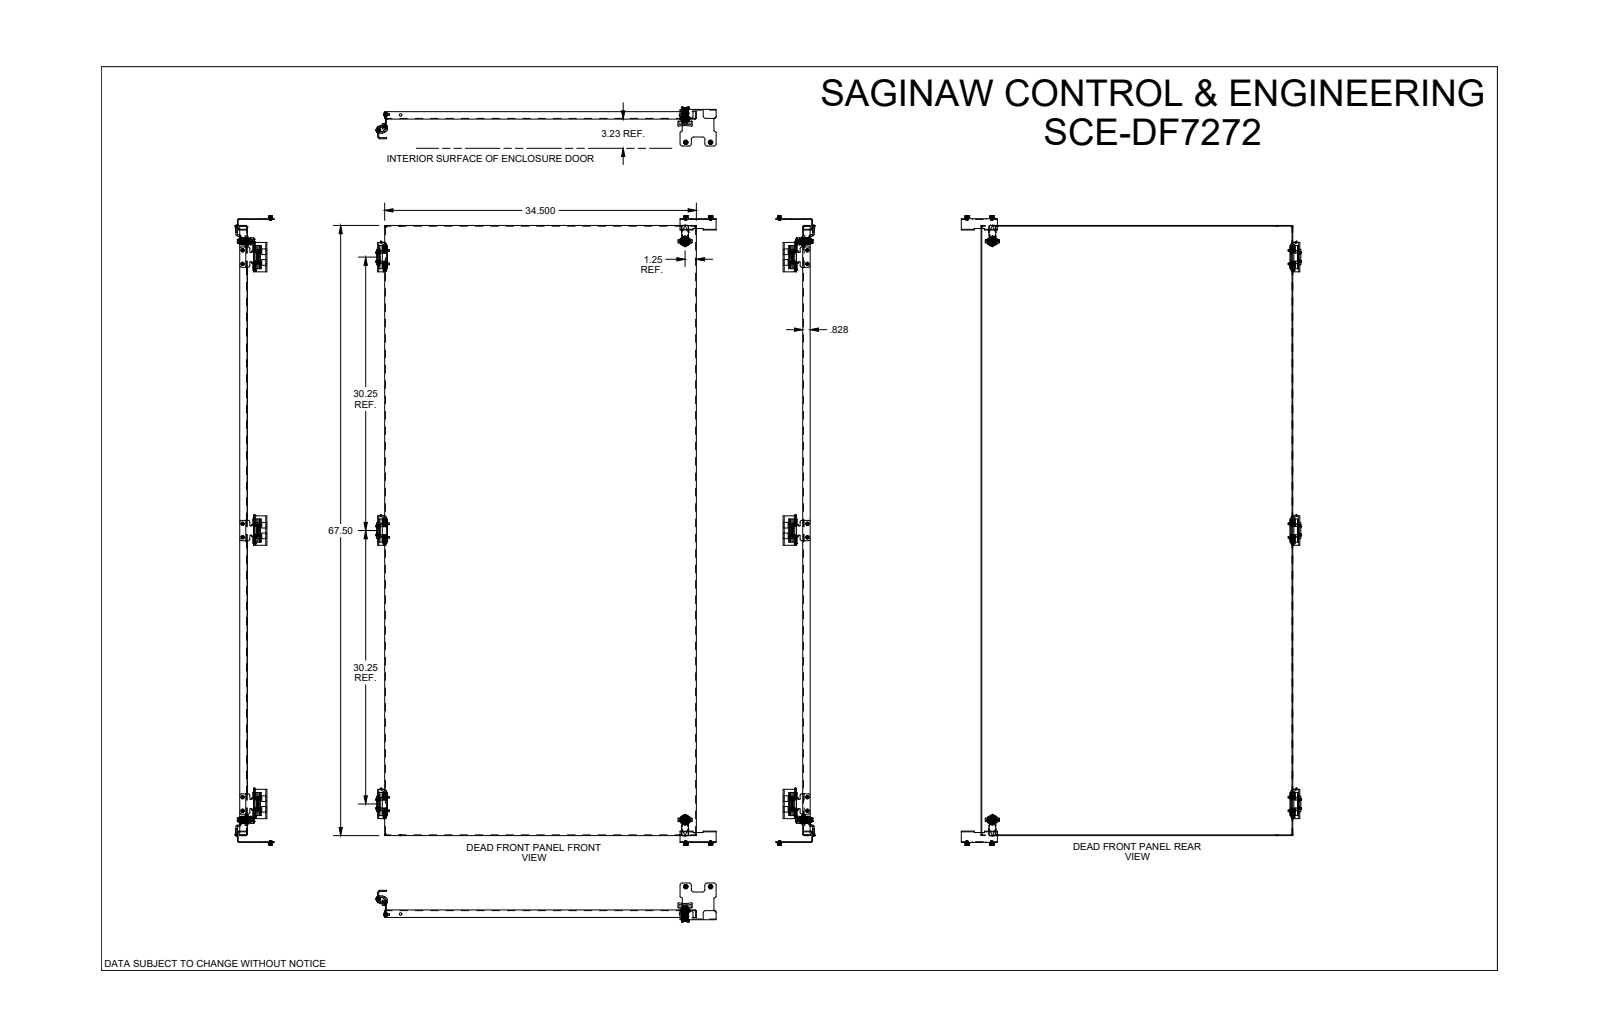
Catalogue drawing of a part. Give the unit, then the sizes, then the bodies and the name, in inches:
Units: inches
Overall size (bounding box): 69.688 × 37.679 × 4.32
Round holes (diameter × count): ⌀0.19 ×8, ⌀0.172 ×6, ⌀0.21 ×6, ⌀0.244 ×6, ⌀0.25 ×6, ⌀0.266 ×6, ⌀0.197 ×2, ⌀0.315 ×2, ⌀0.394 ×2, ⌀0.433 ×2, ⌀0.634 ×2, ⌀0.222 ×1
Round bosses / shafts (diameter × count): ⌀0.17 ×8, ⌀0.373 ×6, ⌀0.34 ×6, ⌀0.25 ×6, ⌀0.249 ×6, ⌀0.188 ×6, ⌀0.196 ×4, ⌀1.102 ×2
Partial cylindrical surfaces — rounded edges, fillets, slot ends (radius × count): R0.012 ×56, R0.25 ×23, R0.02 ×18, R0.157 ×16, R0.062 ×14, R0.01 ×13, R0.068 ×9, R0.125 ×9
Main face-to-face distances: 0.06, 34.44, 67.44, 34.5, 34.38, 0.078, 0.672, 0.732, 68.112, 68.172
Hole centre spacings: 30.25, 0.985, 1.749, 1.75, 2.13, 2.13, 60.5, 29.059
Volume: 160.4 in³ · Surface area: 5 222 in²
Bodies: 54 solids, 2199 faces (1058 planar, 642 cylindrical, 499 other)
Part name (STEP PRODUCT): SCE-DF7272
STEP written by: SolidWorks 2021 (AUTOMOTIVE_DESIGN)
